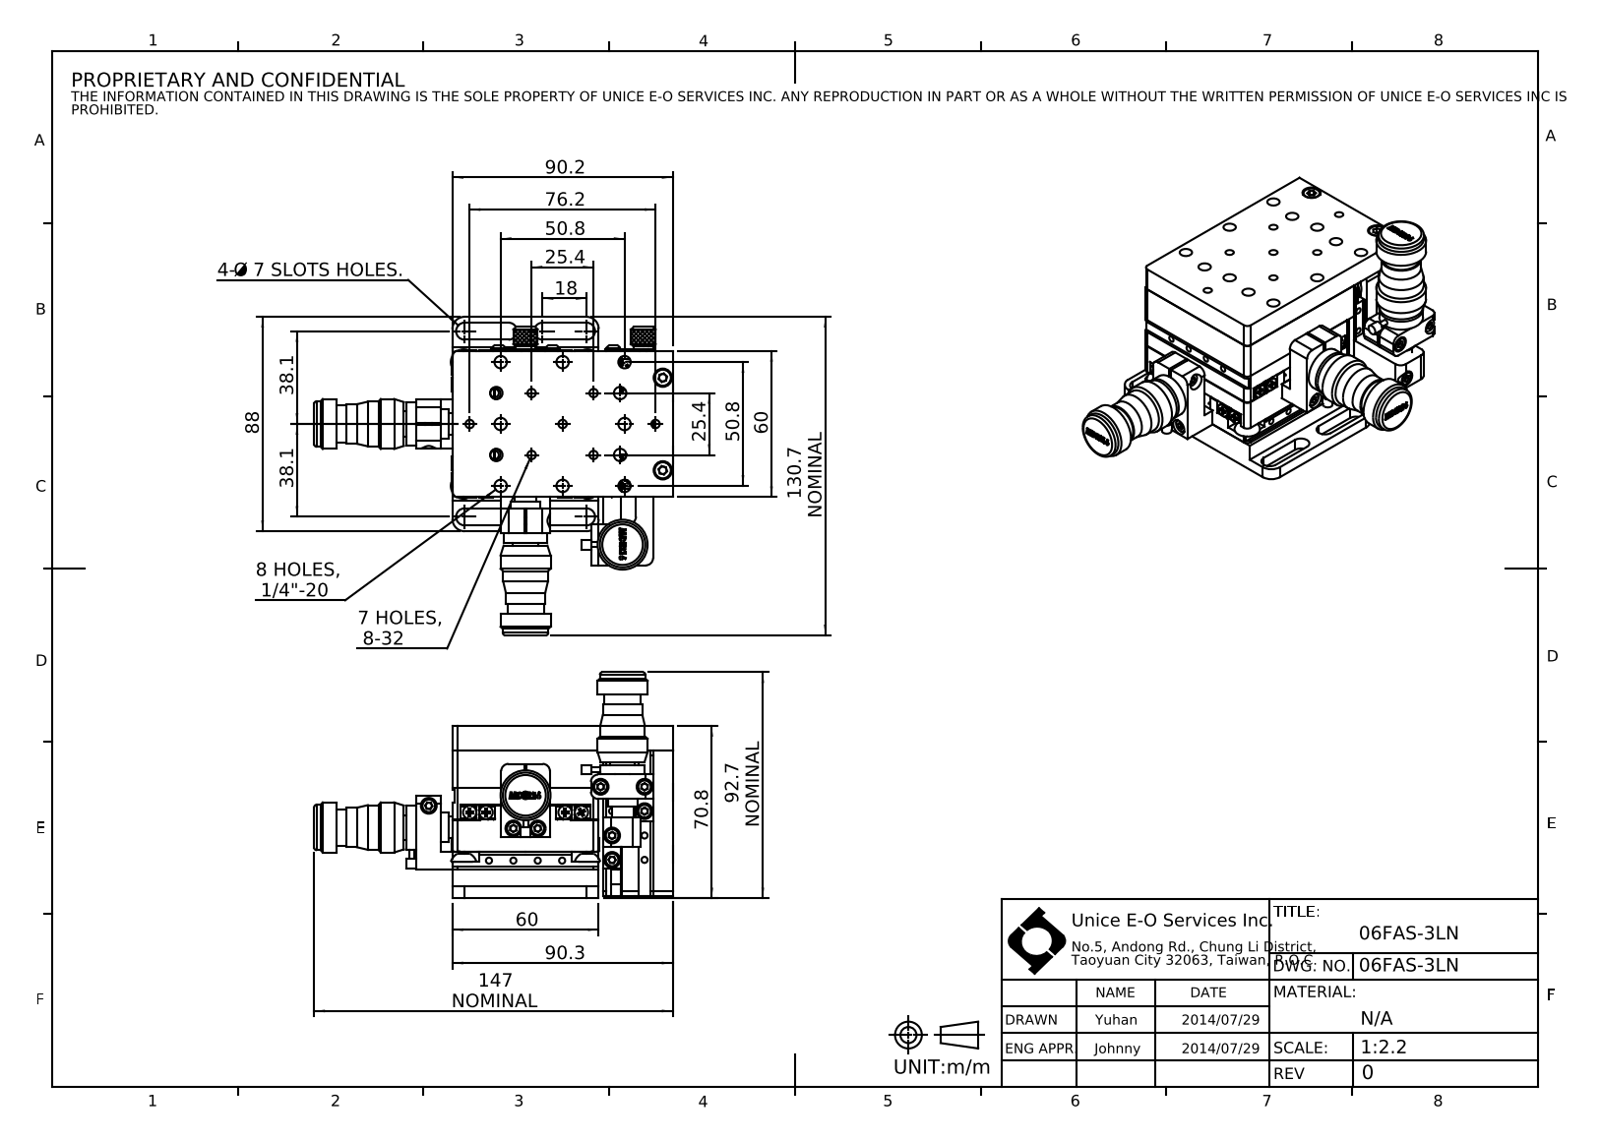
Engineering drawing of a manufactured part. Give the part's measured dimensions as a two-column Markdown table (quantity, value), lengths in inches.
| quantity | value |
| --- | --- |
| part name | 06FAS-3LN |
| STEP written by | SolidWorks 2016 (CONFIG_CONTROL_DESIGN) |
| units | inches |
| bodies | 0 solids, 1483 faces (870 planar, 365 cylindrical, 248 other) |
| overall size | 6.016 × 5.374 × 3.65 |
| round holes (diameter × count) | 0.098 × 18, 0.256 × 13, 0.201 × 12, 0.081 × 8, 0.136 × 7, 0.197 × 6, 0.315 × 4, 0.122 × 2, 0.236 × 2, 0.295 × 2 |
| round bosses / shafts (diameter × count) | 0.217 × 18, 0.276 × 4, 0.224 × 4, 0.807 × 3, 0.734 × 3, 0.721 × 3, 0.709 × 3, 0.637 × 3 |
| partial cylindrical surfaces (radius × count) | 0.079 × 12, 0.118 × 11, 0.138 × 8, 0.069 × 4, 0.197 × 4 |
| main face-to-face distances | 0.276, 0.799, 1.921, 0.516, 0.524, 0.52, 2.394, 0.394, 2.362, 2.315 |
| hole center spacings | 1, 0.394, 0.707, 1.581, 1.414, 2.236, 0.984, 0.505 |
